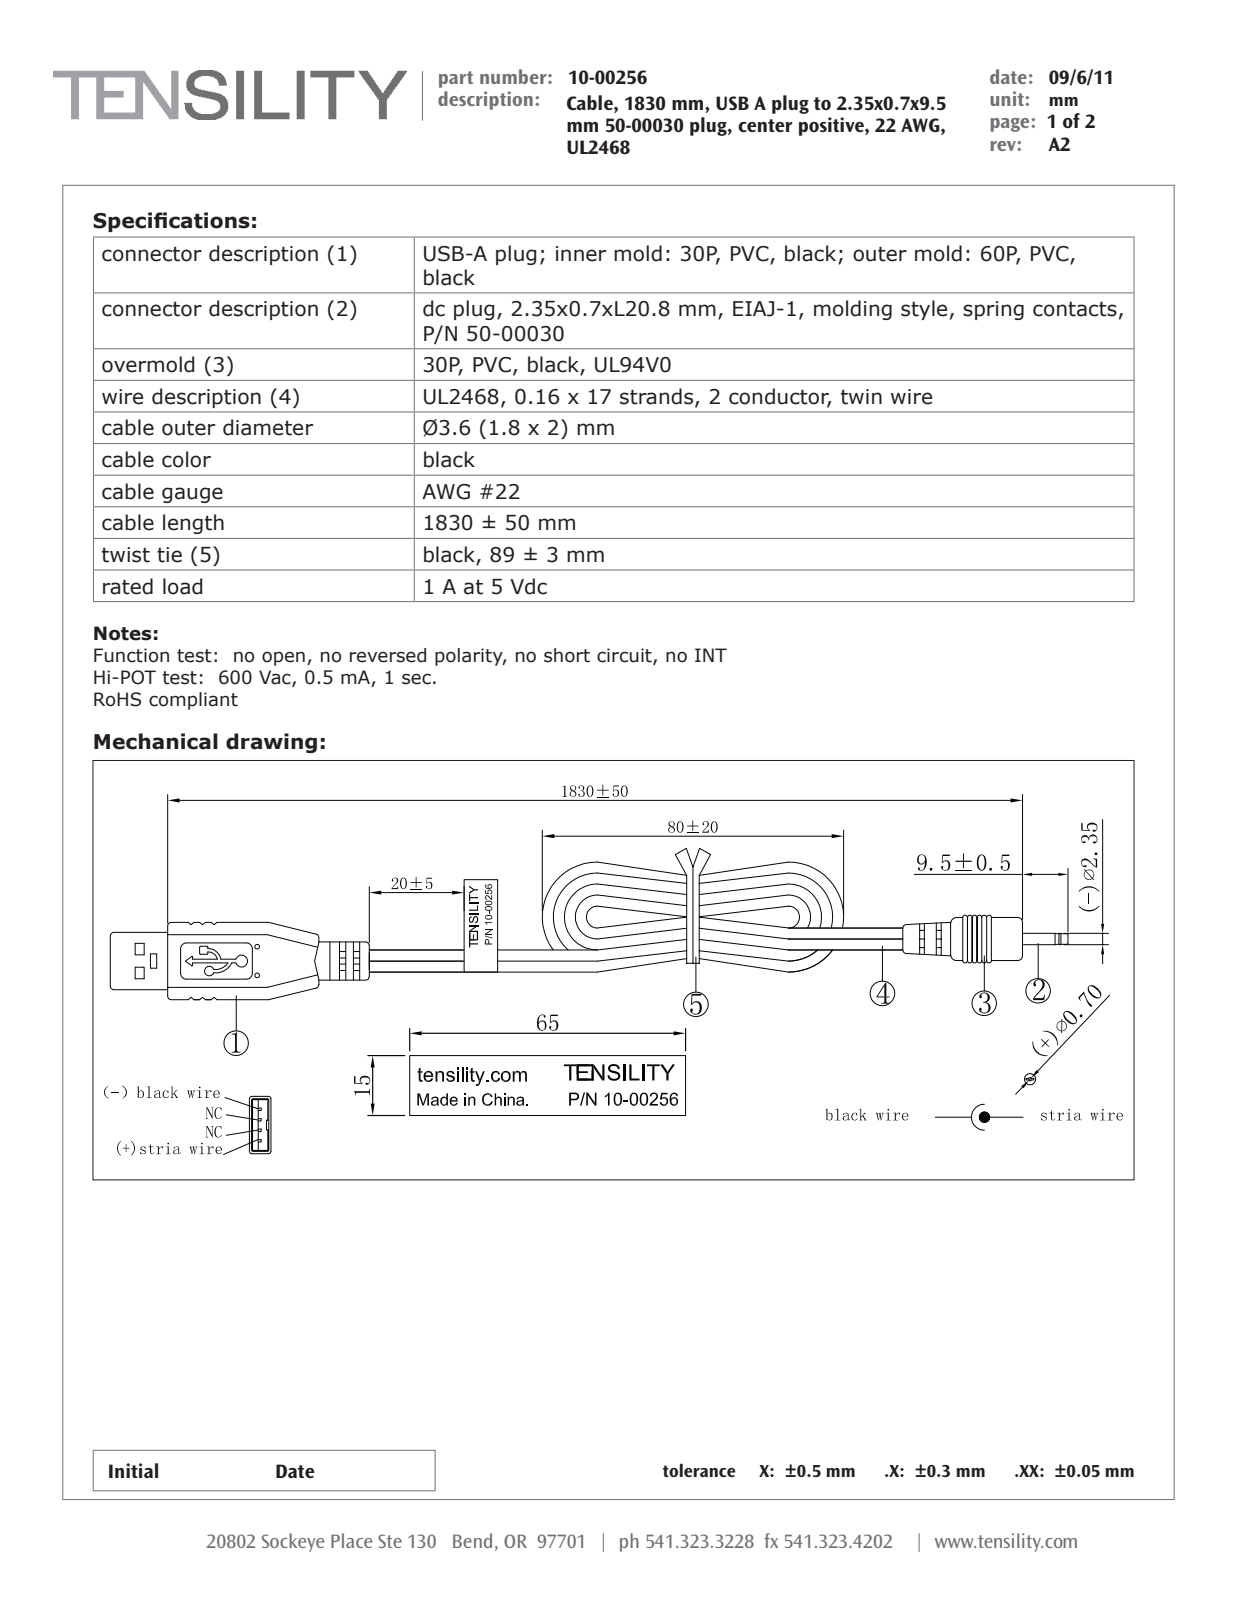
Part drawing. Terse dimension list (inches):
name: 24-00023; 24-00047; 50-00030 block; 50-00425 (+8 more)
written by: SolidWorks 2015 (AUTOMOTIVE_DESIGN)
unit: in
bodies: 59 solids, 1132 faces (568 planar, 273 cylindrical, 291 other)
size: 8.831 × 1.522 × 0.394
volume: 0.457 in³; area: 19.56 in²
holes: 2× ⌀0.033, 1× ⌀0.028, 1× ⌀0.031, 1× ⌀0.047, 1× ⌀0.047, 1× ⌀0.077, 1× ⌀0.093, 1× ⌀0.15
bosses: 2× ⌀0.075, 1× ⌀0.354, 1× ⌀0.315, 1× ⌀0.286, 1× ⌀0.177, 1× ⌀0.161, 1× ⌀0.157, 1× ⌀0.094
rounds: 26× R0.004, 20× R0.008, 10× R0.02, 8× R0.03, 4× R0.012, 4× R0.025, 4× R0.051, 4× R0.315
face distances: 0.077, 0.073, 0.071, 0.079, 0.254, 0.177, 0.092, 0.152, 0.081, 0.013
hole spacings: 0.035, 0.07
